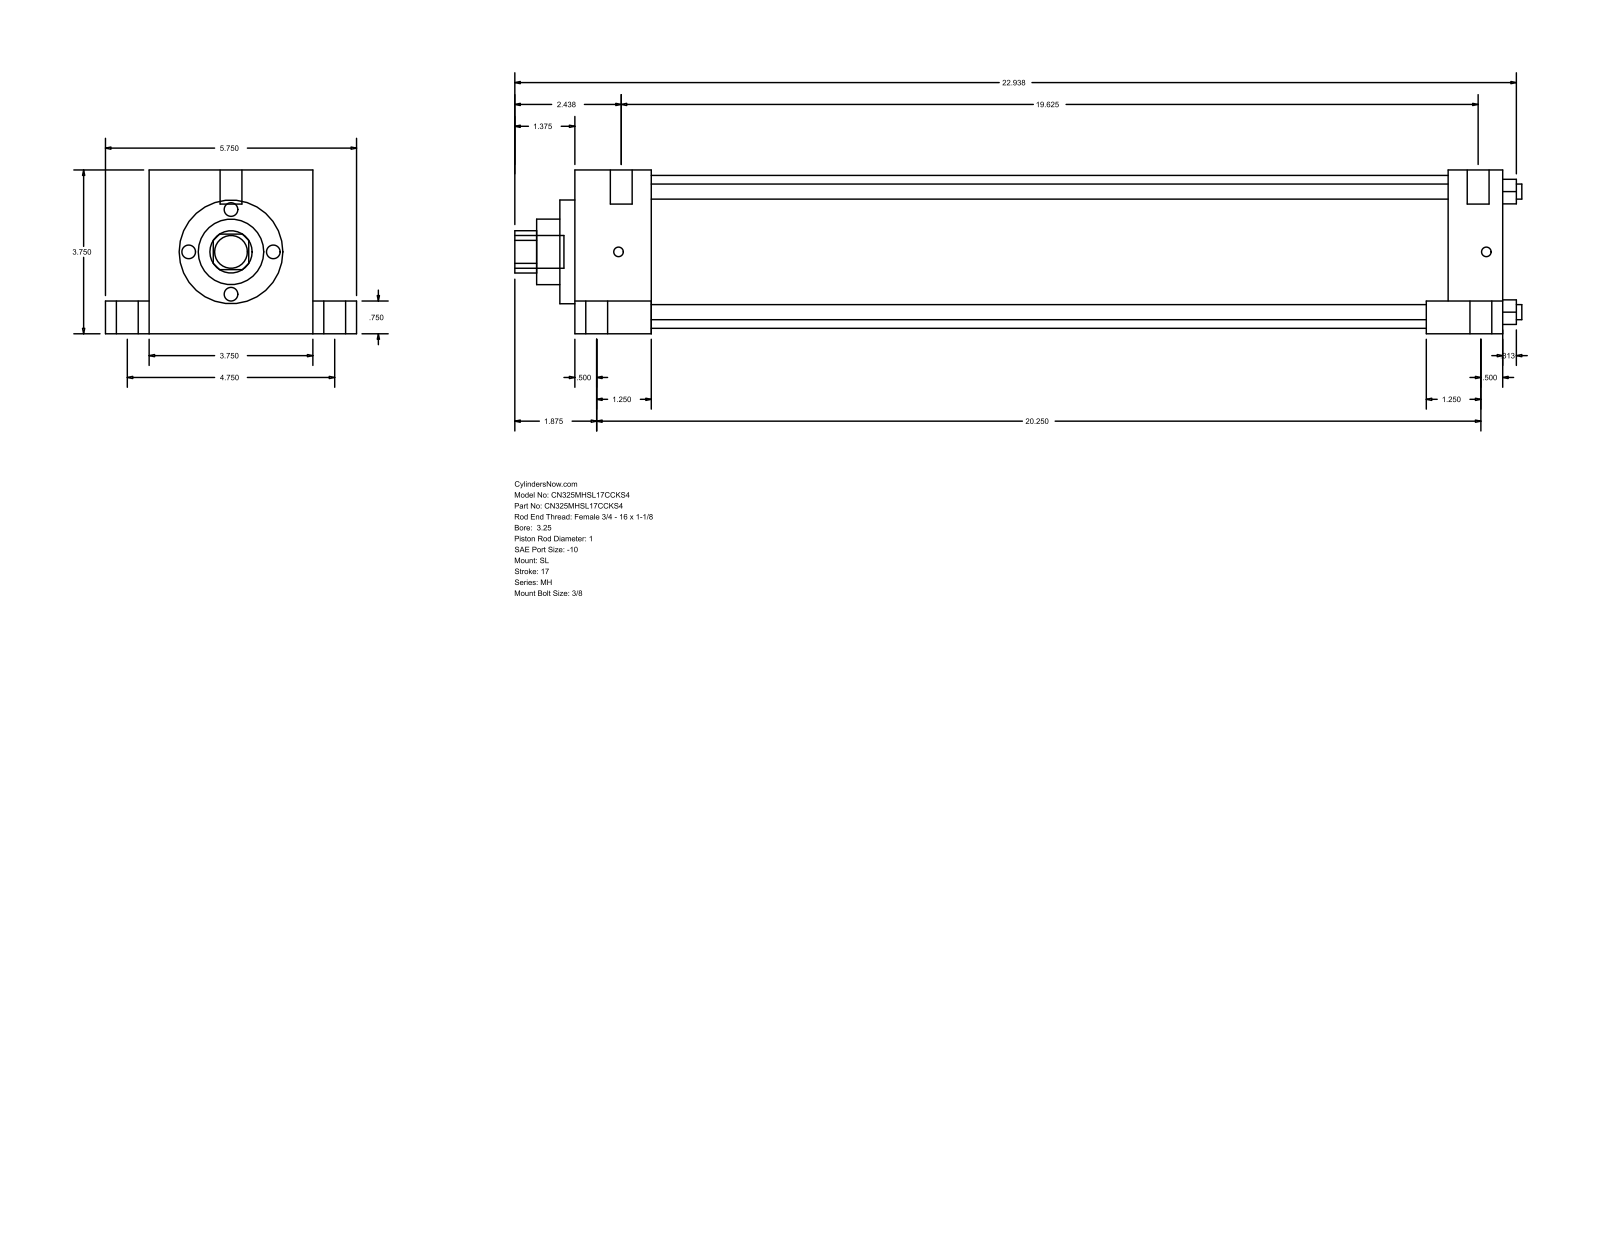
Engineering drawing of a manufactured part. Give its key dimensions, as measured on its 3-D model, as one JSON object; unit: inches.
{"part_name": "MH_SL__0325_1", "step_written_by": "GSSL Pune (CONFIG_CONTROL_DESIGN)", "units": "inches", "bodies": {"solids": 0, "faces": 110, "planar": 77, "cylindrical": 33, "other": 0}, "overall_size": [23.063, 5.75, 3.75], "round_holes": [[0.345, 4], [1, 1], [1.5, 1], [2.375, 1], [3.5, 1]], "round_bosses_or_shafts": [[0.5, 6], [0.75, 5], [0.219, 4]], "partial_cylinders_radius": [[0.484, 1]], "face_to_face_distances": [3.75, 21.25, 1.75, 19.5, 1, 4.75, 0.75, 3, 20, 18.25], "hole_center_spacings": [1.952, 2.76, 3.903]}
